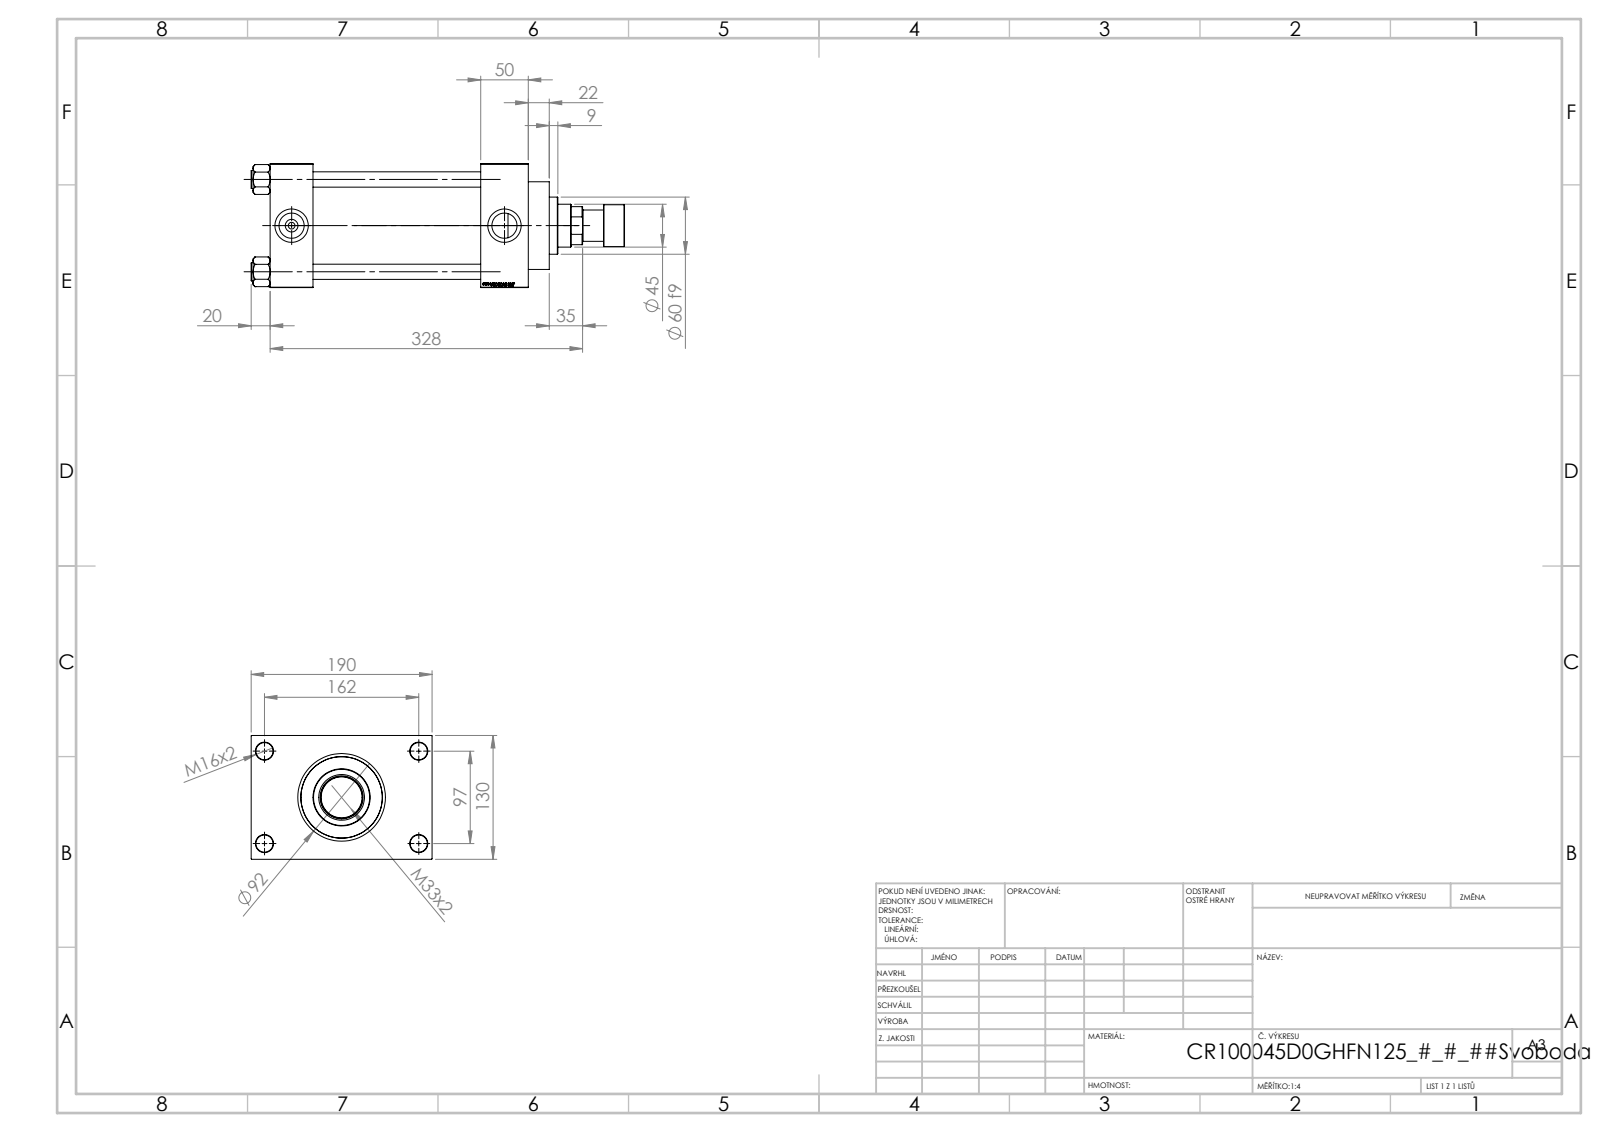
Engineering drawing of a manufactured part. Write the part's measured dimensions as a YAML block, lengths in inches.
part_name: "V215_VC_A; V215CR_VCP_D; V215CR_ROD_END_F; V215CR_D_TYCINKA (+2 more)"
step_written_by: "SolidWorks 2019 (CONFIG_CONTROL_DESIGN)"
units: inches
bodies: {solids: 12, faces: 1164, planar: 548, cylindrical: 92, other: 524}
overall_size: [15.433, 7.48, 5.118]
volume: 182.8
surface_area: 724.1
round_holes:
  - {diameter: 0.63, count: 4}
  - {diameter: 0.709, count: 4}
  - {diameter: 0.276, count: 2}
  - {diameter: 1.041, count: 2}
  - {diameter: 1.378, count: 2}
  - {diameter: 1.24, count: 1}
  - {diameter: 1.772, count: 1}
  - {diameter: 1.89, count: 1}
  - {diameter: 2.992, count: 1}
  - {diameter: 3.366, count: 1}
  - {diameter: 3.937, count: 1}
round_bosses_or_shafts:
  - {diameter: 0.748, count: 4}
  - {diameter: 4.173, count: 1}
  - {diameter: 3.622, count: 1}
  - {diameter: 2.362, count: 1}
  - {diameter: 1.732, count: 1}
  - {diameter: 1.299, count: 1}
face_to_face_distances: [5.118, 1.772, 8.701, 6.929, 10.669, 8.898, 1.969, 1.181, 6.299, 4.921]
hole_center_spacings: [1.281, 2.698, 3.717, 3.815, 4.026, 5.096, 6.367, 3.819]
